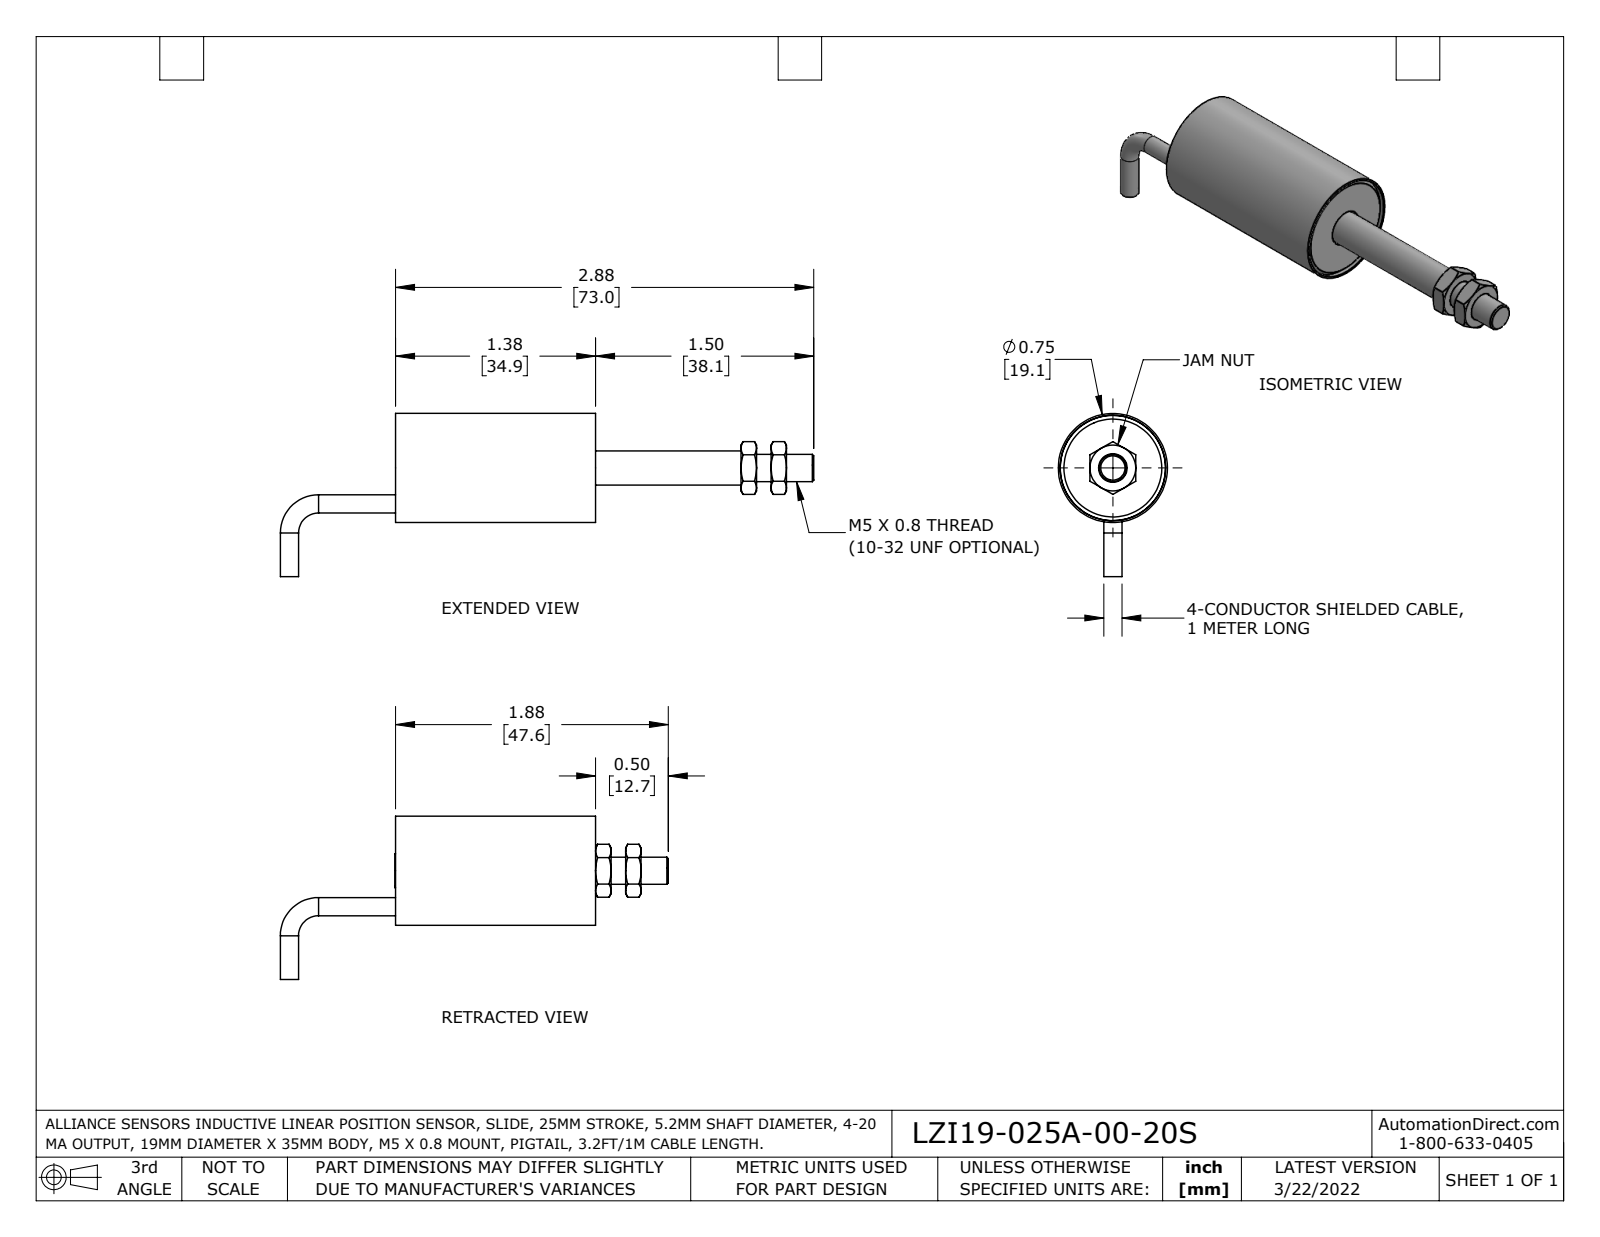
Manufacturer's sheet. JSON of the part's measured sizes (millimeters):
{"part_name": "3120-0009-06_-01; 3120-0008-06_-01; 5500-0031; 3300-0008-06_-01 (+6 more)", "step_written_by": "SolidWorks 2021 (AUTOMOTIVE_DESIGN)", "units": "millimeters", "bodies": {"solids": 10, "faces": 137, "planar": 42, "cylindrical": 44, "other": 51}, "overall_size": [93.2, 28.5, 19.1], "volume_mm3": 4920, "surface_area_mm2": 9968, "round_holes": [[4.2, 1], [4.8, 1], [5, 1], [5.9, 1], [7.1, 1], [17.3, 1], [18.4, 1]], "round_bosses_or_shafts": [[3.2, 2], [19.1, 1], [18.4, 1], [7.1, 1], [4.7, 1]], "partial_cylinders_radius": [[1.3, 1]], "face_to_face_distances": [1.5, 32.9, 2, 31.4, 34.4, 8, 5.2, 2.7, 9.5, 2.5]}
